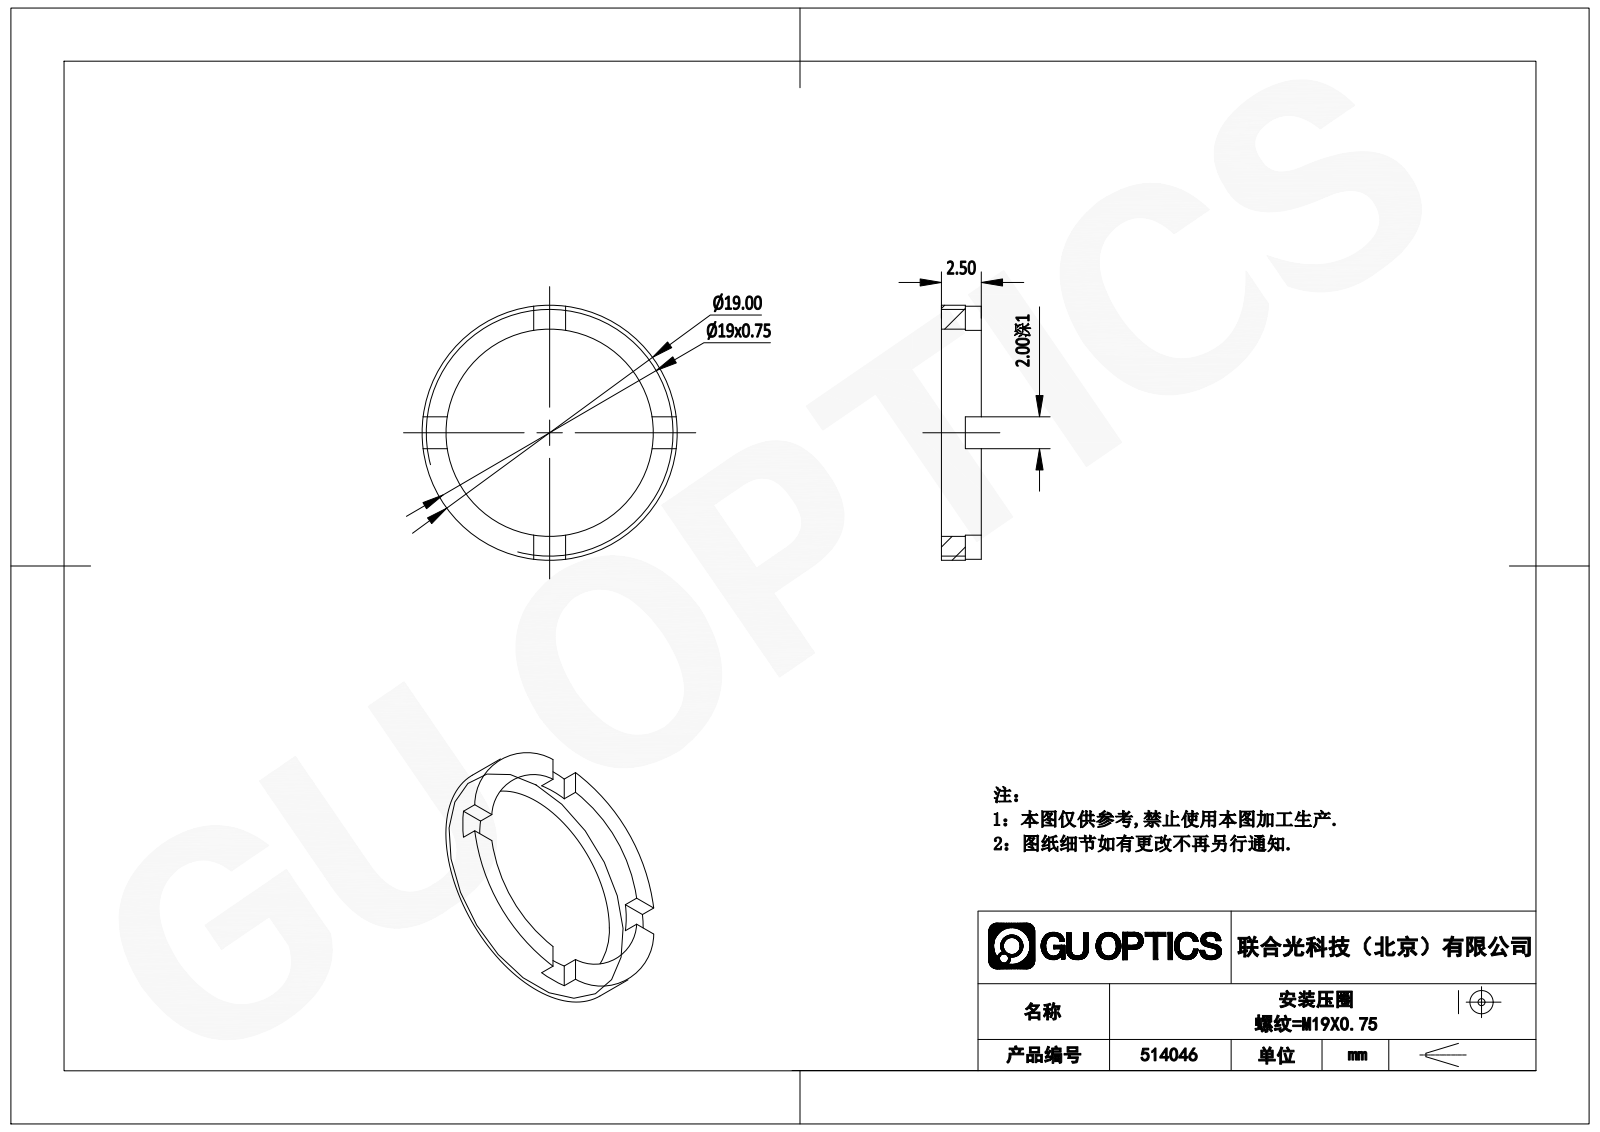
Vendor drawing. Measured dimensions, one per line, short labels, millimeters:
name: 514046
written by: SolidWorks 2020 (CONFIG_CONTROL_DESIGN)
unit: mm
bodies: 1 solid, 21 faces (17 planar, 4 cylindrical, 0 other)
size: 19 × 19 × 2.5
volume: 194 mm³; area: 436 mm²
holes: 1× ⌀16
bosses: 1× ⌀19
face distances: 2.5, 1.5, 1, 2
